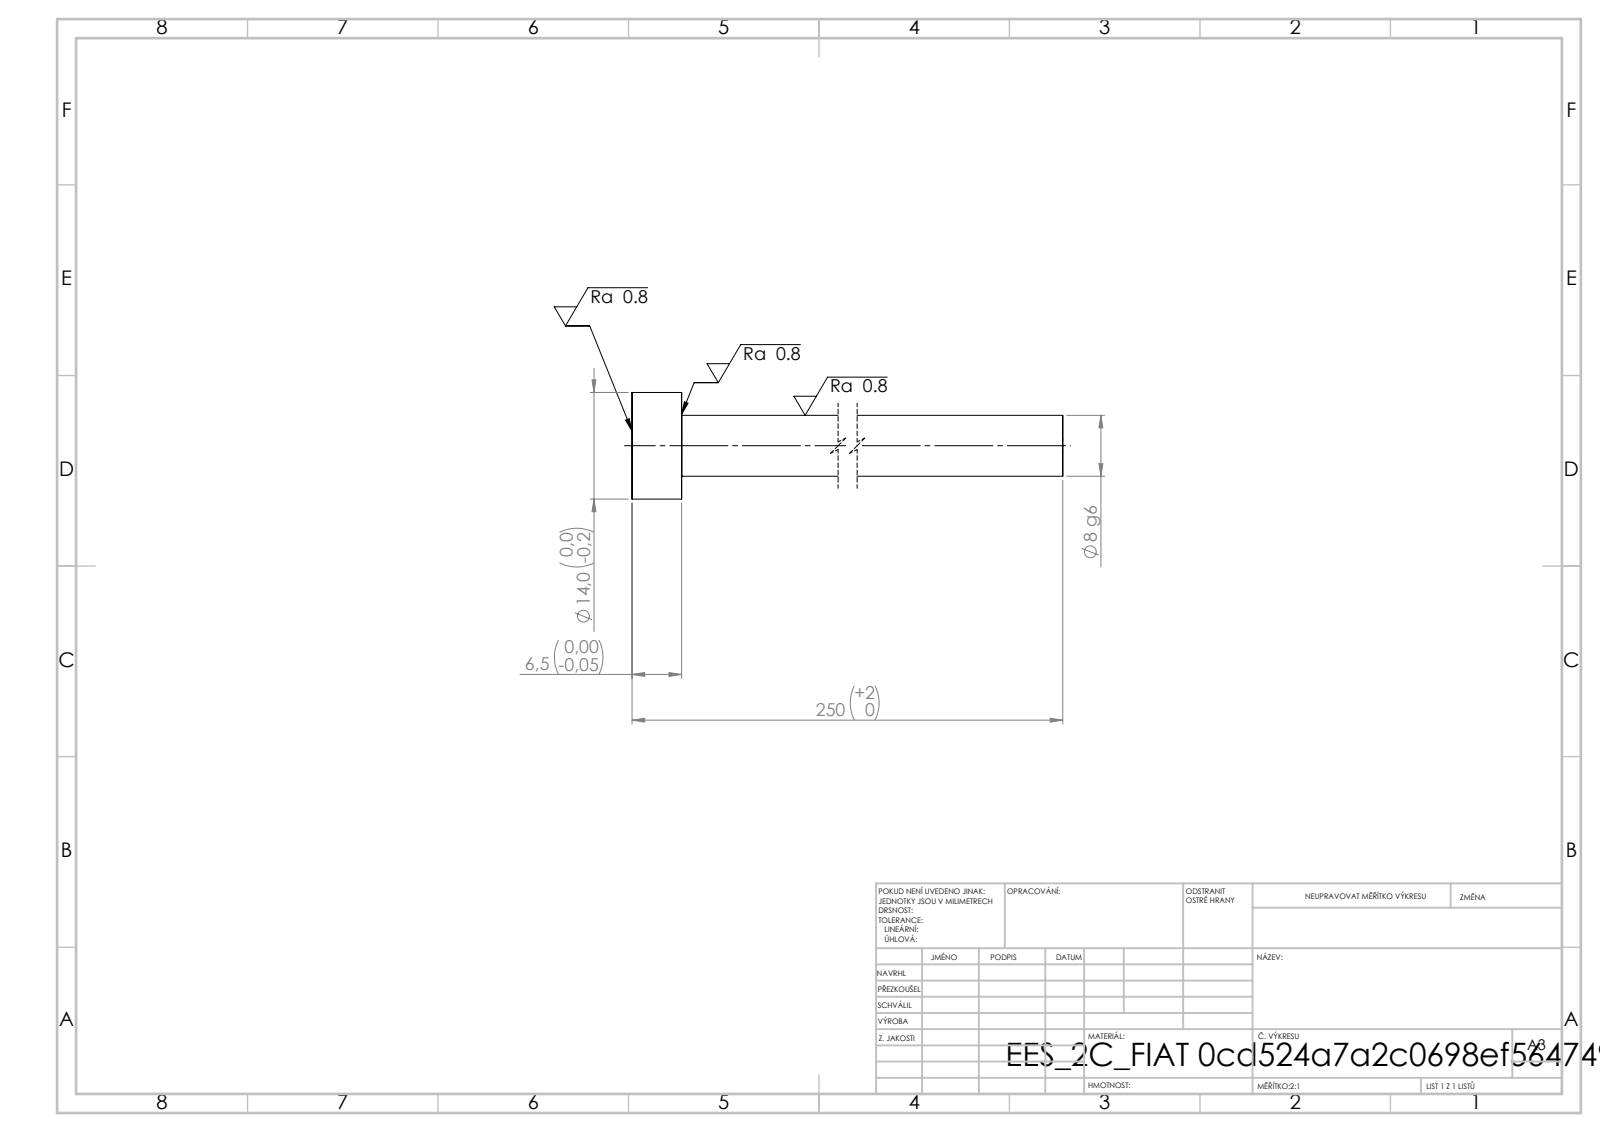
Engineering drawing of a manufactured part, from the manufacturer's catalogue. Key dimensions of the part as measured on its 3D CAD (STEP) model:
STEP written by: SolidWorks 2019 (CONFIG_CONTROL_DESIGN)
Units: millimetres
Bodies: 1 solid, 7 faces (3 planar, 4 cylindrical, 0 other)
Overall size (bounding box): 250 × 14 × 14
Volume: 13 240 mm³ · Surface area: 6 714 mm²
Round bosses / shafts (diameter × count): ⌀14 ×1, ⌀8 ×1
Main face-to-face distances: 6.5, 250, 243.5
